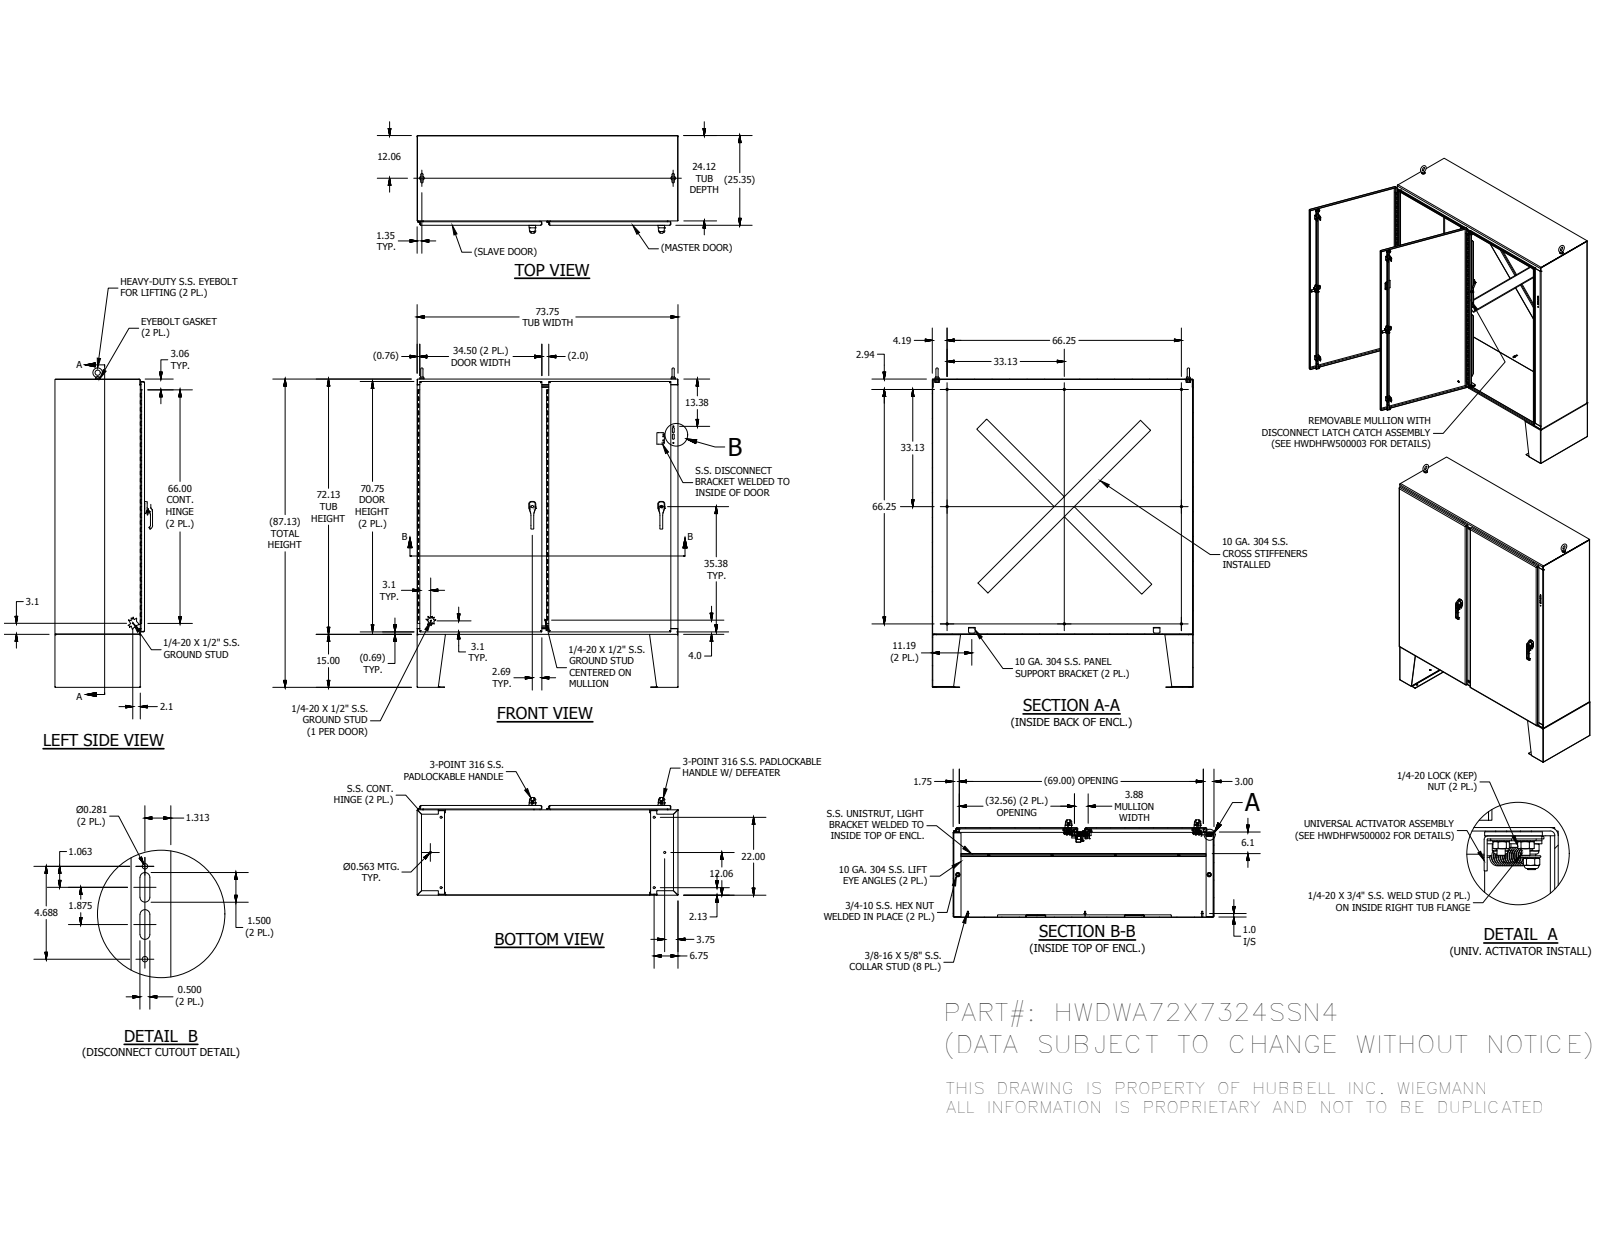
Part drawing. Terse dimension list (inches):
name: WA72X7324SSN4BLR; WAX7324SSN4TOP; WAX7324SSN4BTM; HFW332010S (+8 more)
written by: Autodesk Inventor 2016 (AUTOMOTIVE_DESIGN)
unit: in
bodies: 220 solids, 9190 faces (4286 planar, 3104 cylindrical, 1800 other)
size: 90.248 × 73.75 × 27.596
volume: 2 382 in³; area: 45 660 in²
holes: 18× ⌀0.375, 18× ⌀0.563, 17× ⌀0.25, 9× ⌀0.187, 8× ⌀0.19, 8× ⌀0.196, 8× ⌀0.262, 8× ⌀0.289, 8× ⌀0.335, 8× ⌀0.38, 6× ⌀0.156, 6× ⌀0.213
bosses: 20× ⌀0.25, 18× ⌀0.33, 13× ⌀0.625, 12× ⌀0.337, 11× ⌀0.375, 9× ⌀0.563, 8× ⌀0.28, 6× ⌀1
rounds: 359× R0.02, 221× R0.012, 192× R0.02, 55× R0.125, 42× R0.019, 28× R0.05, 28× R0.079, 23× R0.25
face distances: 0.104, 25.244, 25.14, 25.348, 72.021, 73.646, 71.917, 73.542, 72.125, 73.75
hole spacings: 0.38, 0.76, 1.195, 5, 9.835, 22.75, 23.293, 34.888
